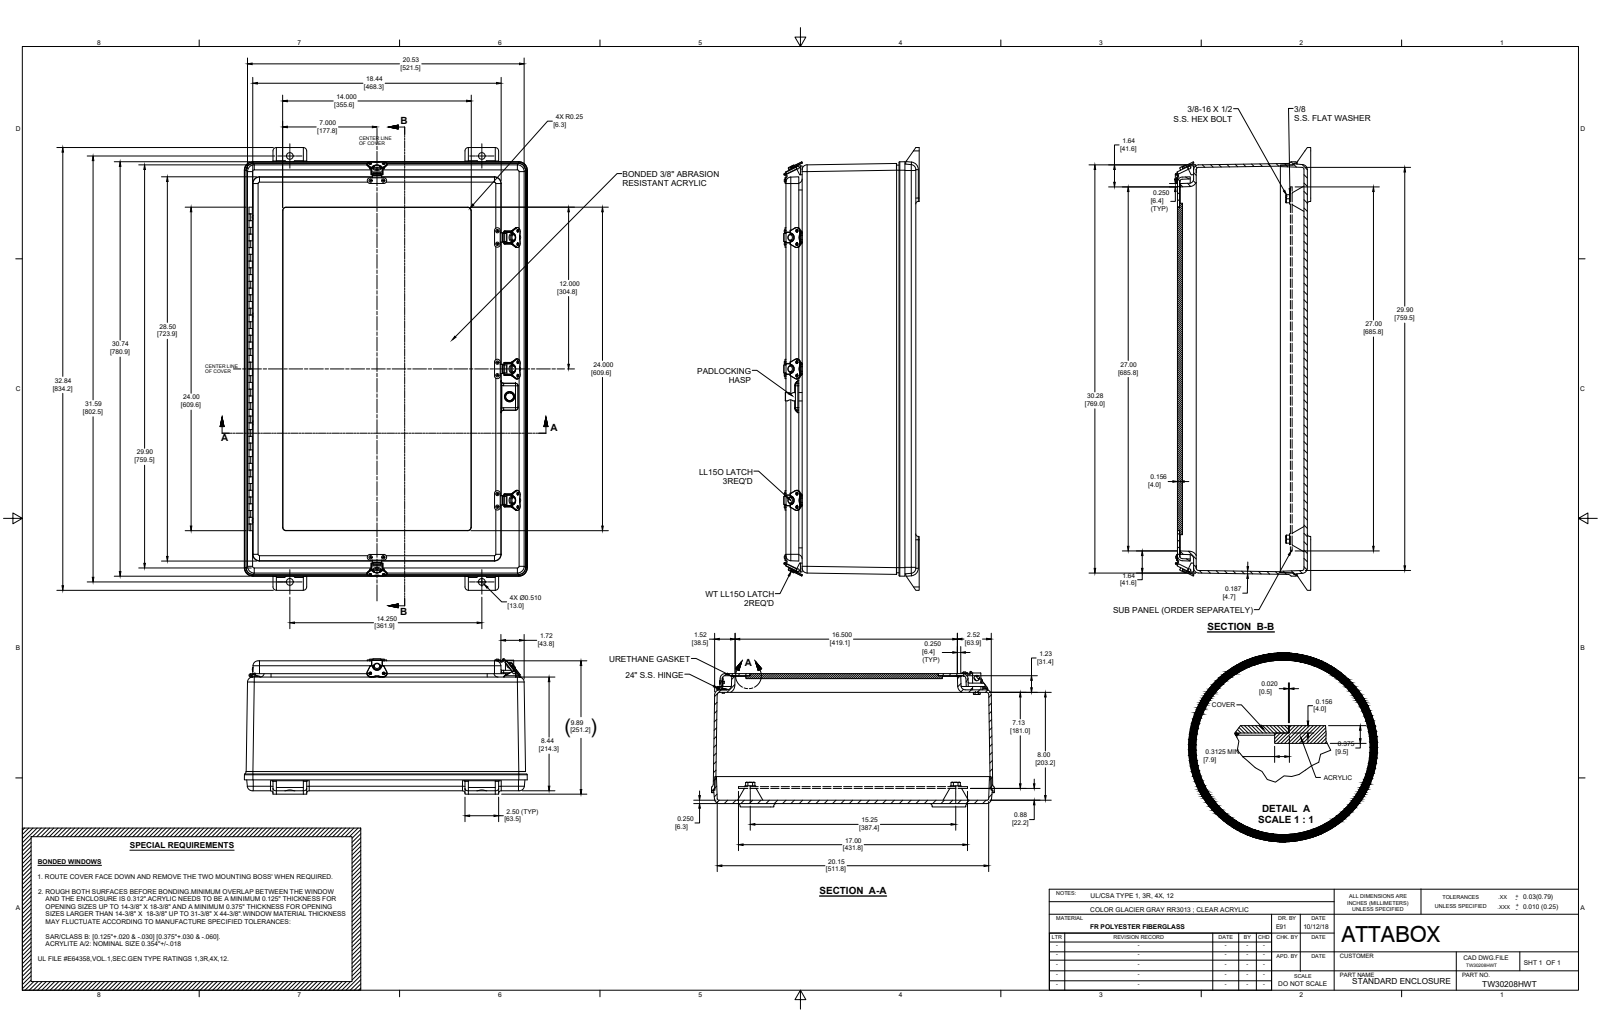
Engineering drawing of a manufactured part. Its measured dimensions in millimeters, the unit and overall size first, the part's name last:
Units: millimetres
Overall size (bounding box): 834.2 × 533.4 × 255.4
Round holes (diameter × count): ⌀3.3 ×36, ⌀1.6 ×20, ⌀3.5 ×10, ⌀4.7 ×10, ⌀1.7 ×5, ⌀7.8 ×4, ⌀14.3 ×4, ⌀1.7 ×3, ⌀4 ×3, ⌀3.4 ×2, ⌀12.7 ×2, ⌀13 ×2
Round bosses / shafts (diameter × count): ⌀3.6 ×20, ⌀7.5 ×8, ⌀12.7 ×5, ⌀5.1 ×3, ⌀6.4 ×1, ⌀5.1 ×1, ⌀3.4 ×1
Partial cylindrical surfaces — rounded edges, fillets, slot ends (radius × count): R0.3 ×127, R6.4 ×28, R0.8 ×20, R4.7 ×18, R9.5 ×17, R7.9 ×15, R12.7 ×12, R3.2 ×10
Main face-to-face distances: 6.4, 4.7, 244.9, 238.6, 235.4, 229.1, 9.5, 4, 241, 234.6
Hole centre spacings: 247.7, 21.1, 38.4, 184.2, 387.4, 495.3, 25.4, 81.6
Volume: 9 183 000 mm³ · Surface area: 3 361 000 mm²
Bodies: 68 solids, 1862 faces (702 planar, 722 cylindrical, 438 other)
Part name (STEP PRODUCT): TW30208HWT
STEP written by: SolidWorks 2018 (AUTOMOTIVE_DESIGN)
